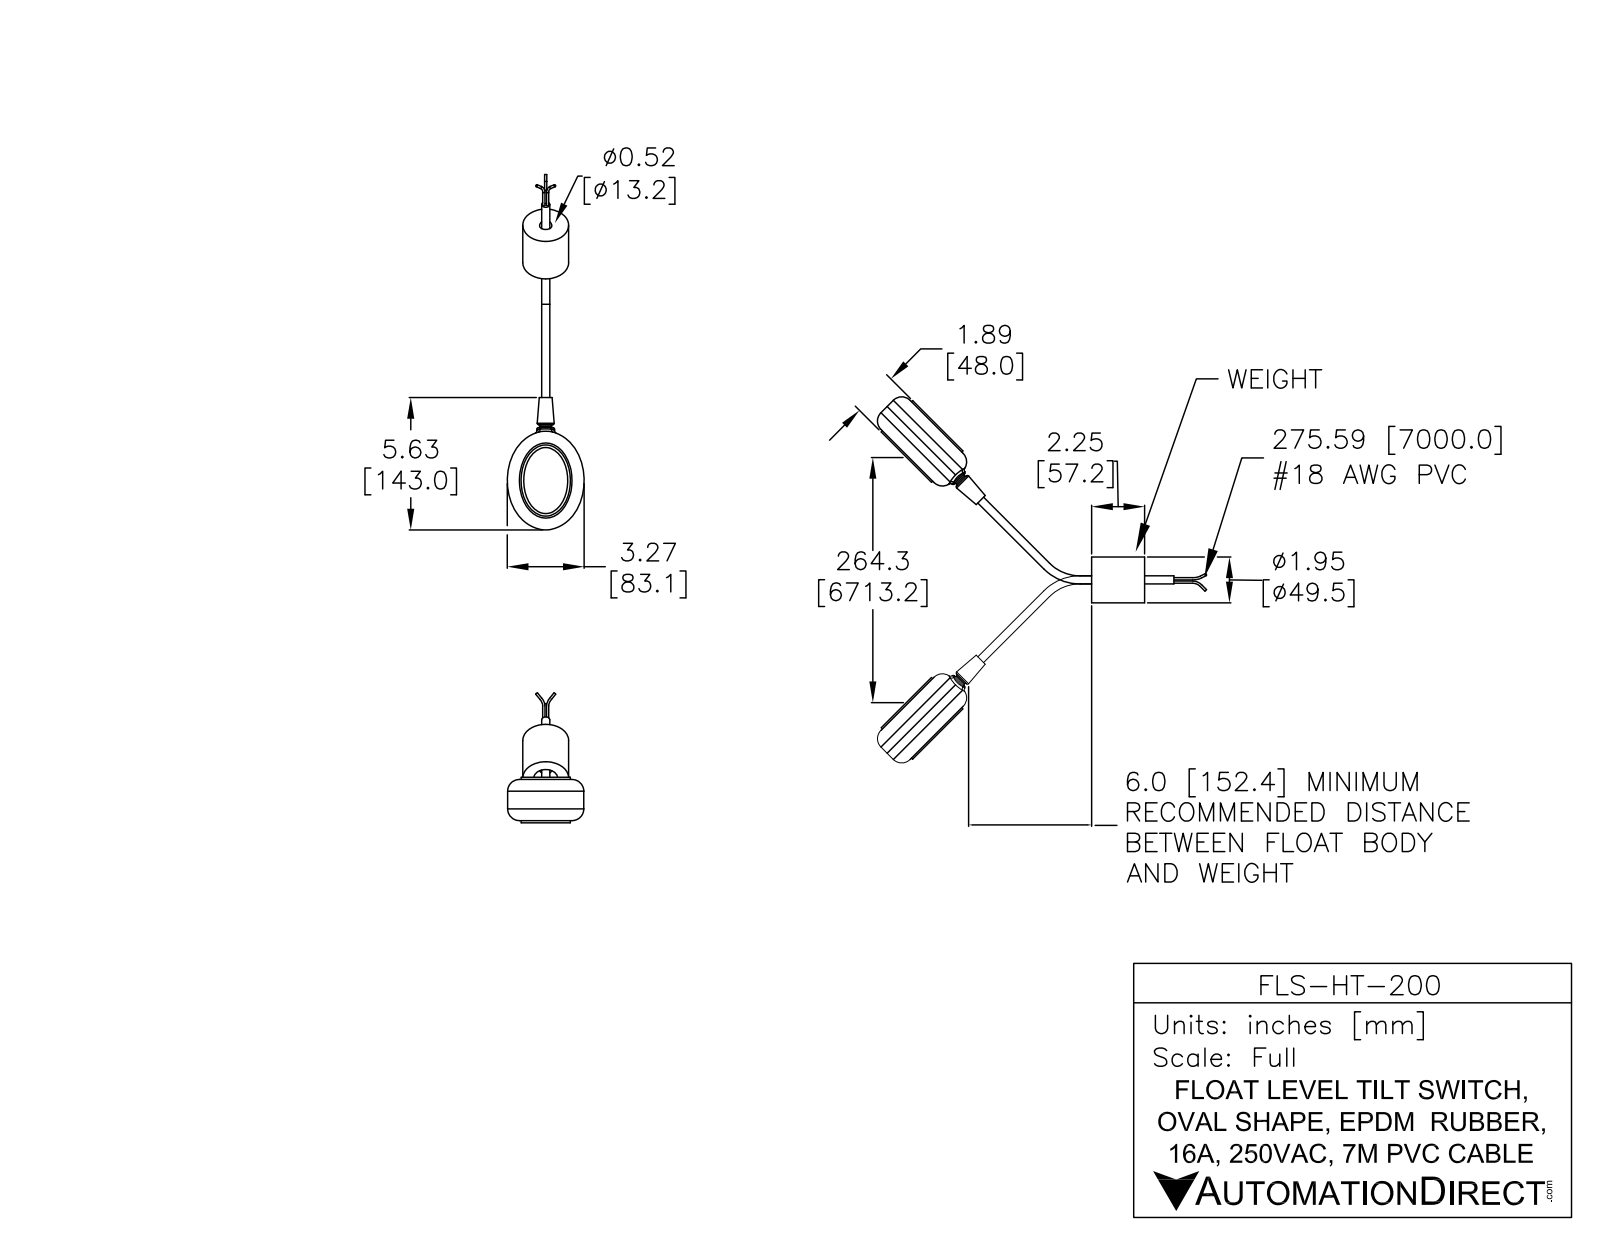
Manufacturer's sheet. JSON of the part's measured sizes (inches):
{"part_name": "FLS-HT-200", "step_written_by": "SolidWorks 2013 (AUTOMOTIVE_DESIGN)", "units": "inches", "bodies": {"solids": 3, "faces": 39, "planar": 10, "cylindrical": 4, "other": 25}, "overall_size": [6.575, 3.27, 1.9], "volume_in3": 16.56, "surface_area_in2": 42.47, "round_bosses_or_shafts": [[0.562, 1], [0.266, 1]], "face_to_face_distances": [1.65, 0.125, 1.775, 1.9, 1.25, 0.094, 1.156, 2.25, 2.156, 1]}
